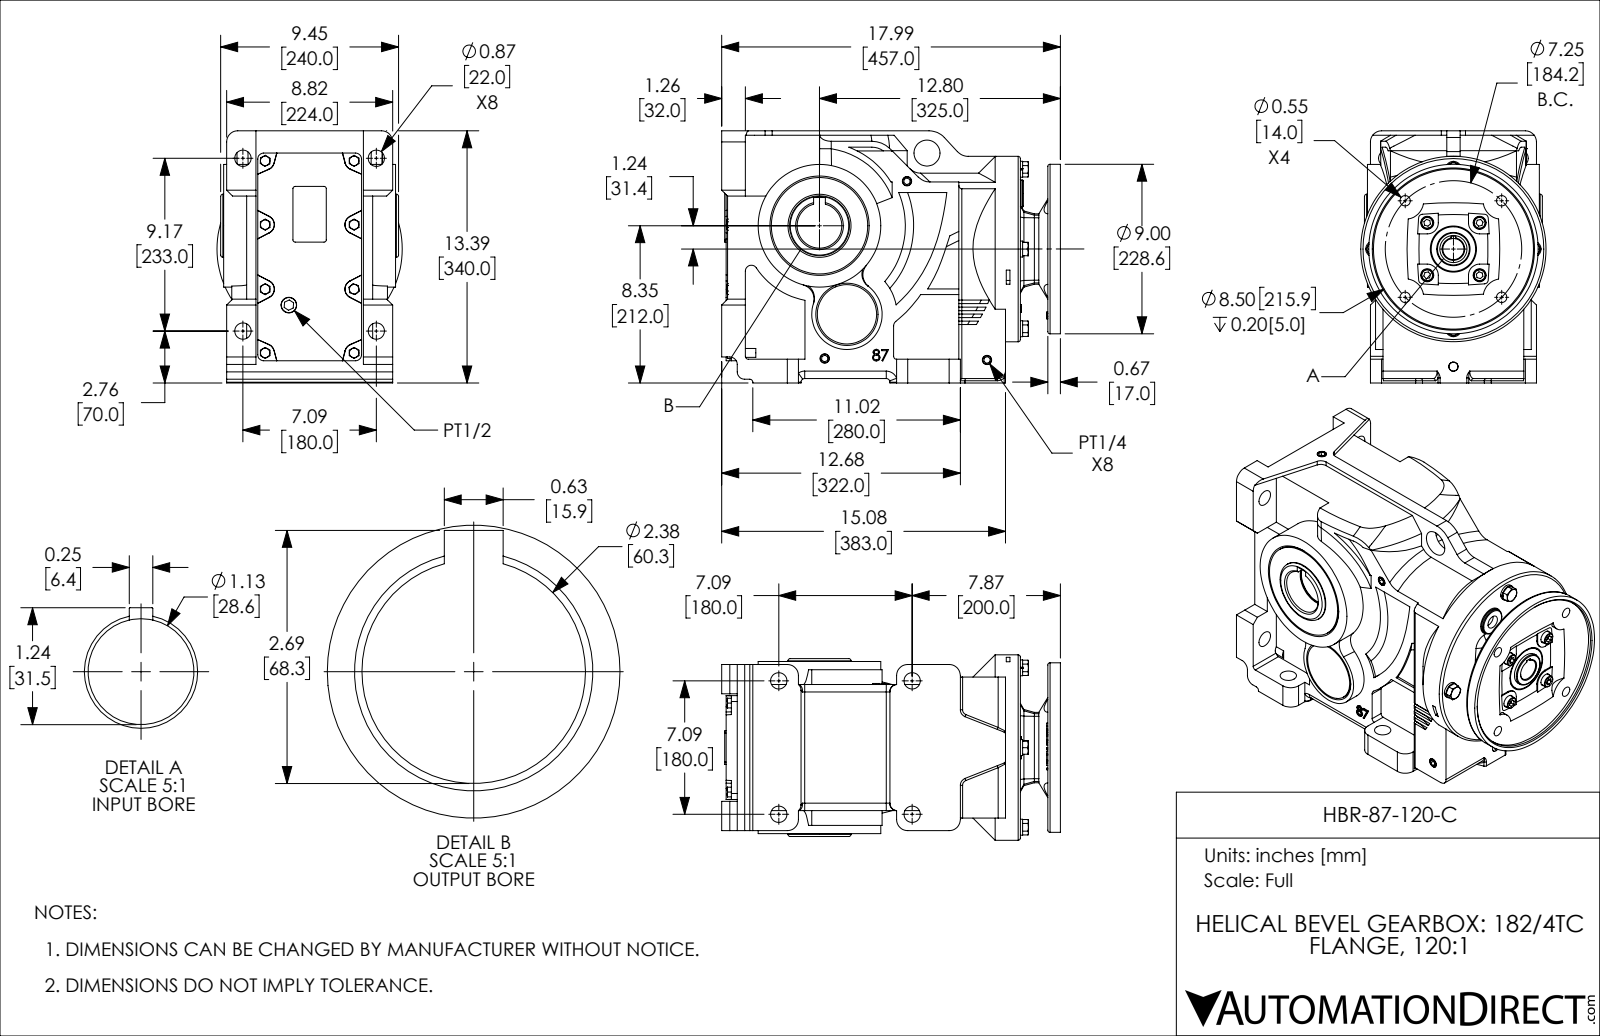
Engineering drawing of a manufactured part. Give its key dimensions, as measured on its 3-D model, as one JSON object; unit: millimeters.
{"part_name": "HBR-87-120-C", "step_written_by": "SolidWorks 2018 (AUTOMOTIVE_DESIGN)", "units": "millimeters", "bodies": {"solids": 8, "faces": 1111, "planar": 542, "cylindrical": 287, "other": 282}, "overall_size": [457, 342.9, 250], "volume_mm3": 22880000, "surface_area_mm2": 844500, "round_holes": [[14, 8], [22, 8], [12.2, 4], [12.6, 4], [17.5, 4], [12, 1], [18, 1], [21, 1], [28.6, 1], [35, 1], [36, 1], [60.3, 1]], "round_bosses_or_shafts": [[21.5, 4], [16, 4], [12, 4], [250, 1], [228.6, 1], [165.4, 1], [130, 1], [85, 1]], "partial_cylinders_radius": [[10, 15], [15, 14], [4, 11], [3, 9], [8, 6], [17.5, 4], [25, 4], [496, 4]], "face_to_face_distances": [17, 6, 153, 27, 37, 180, 334, 10, 397, 31], "hole_center_spacings": [80.3, 180, 184.5, 70.7, 77.7, 104.8, 104.8, 107.5]}
